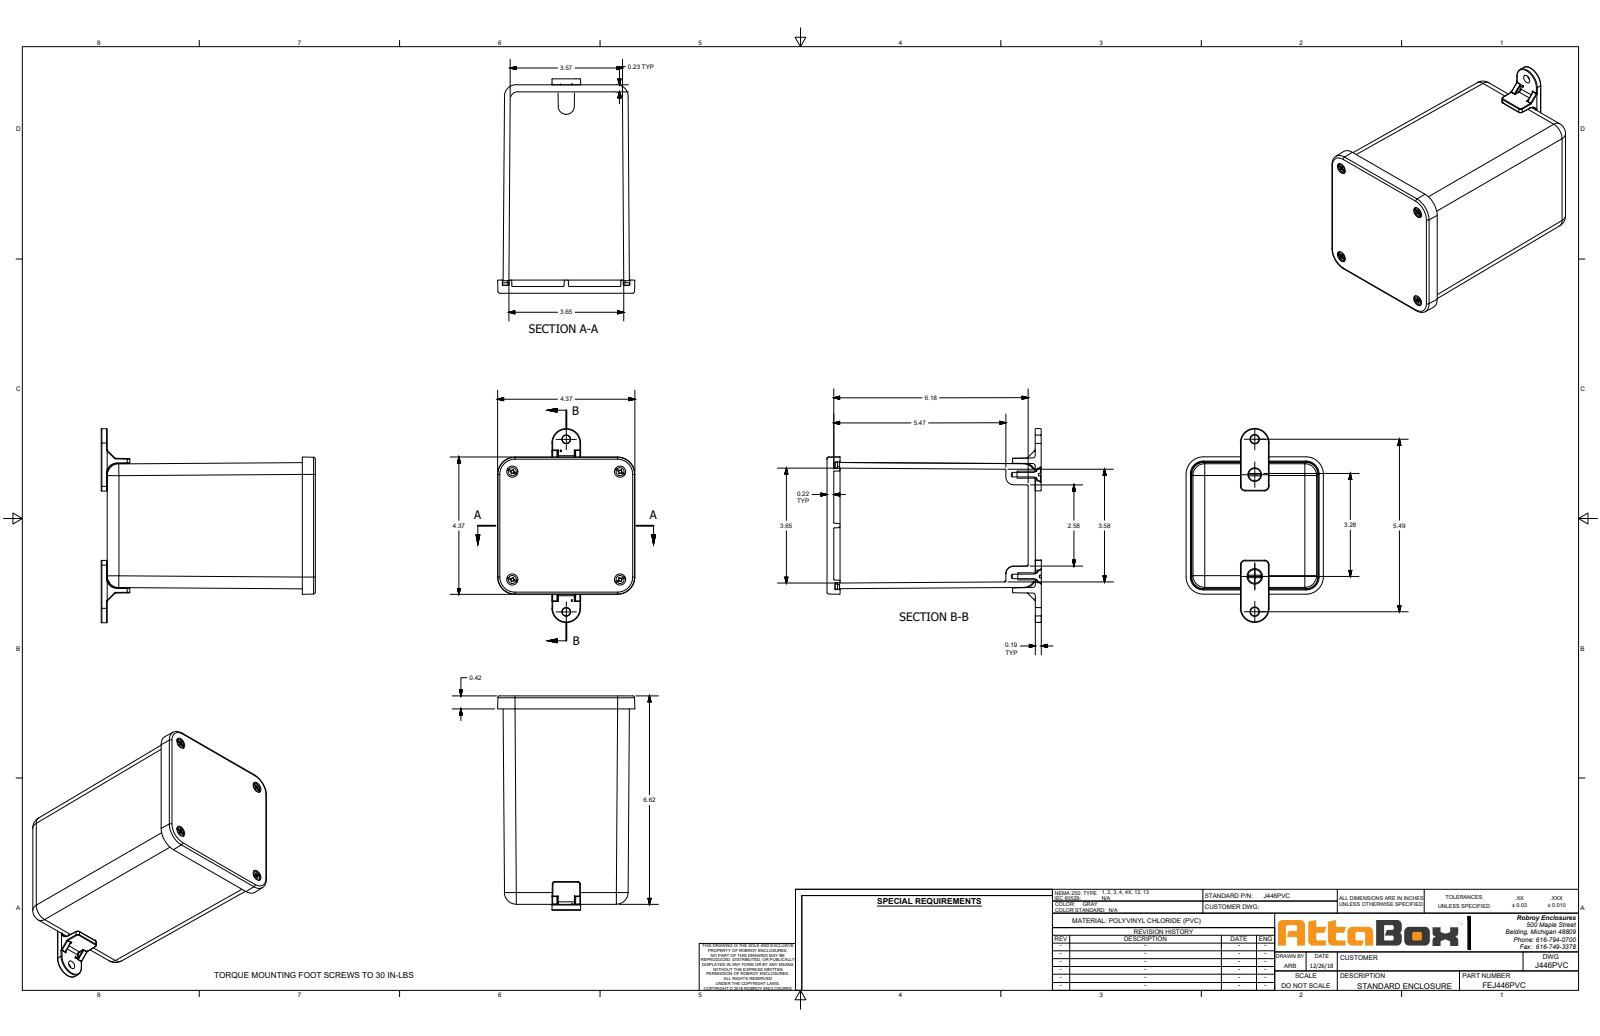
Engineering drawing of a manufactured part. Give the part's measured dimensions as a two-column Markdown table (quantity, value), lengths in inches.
| quantity | value |
| --- | --- |
| part name | J446PVC |
| STEP written by | SolidWorks 2018 (AUTOMOTIVE_DESIGN) |
| units | inches |
| bodies | 19 solids, 945 faces (361 planar, 278 cylindrical, 306 other) |
| overall size | 6.814 × 6.166 × 4.367 |
| volume | 28.15 in³ |
| surface area | 287.9 in² |
| round holes (diameter × count) | 0.2 × 6, 0.13 × 4, 0.18 × 4, 0.187 × 4, 0.223 × 4, 0.25 × 4, 0.335 × 4, 0.35 × 4, 0.166 × 2 |
| round bosses / shafts (diameter × count) | 0.354 × 4, 0.177 × 4, 0.187 × 3, 0.325 × 2, 0.325 × 2, 0.224 × 2 |
| partial cylindrical surfaces (radius × count) | 0.02 × 46, 0.025 × 36, 0.005 × 24, 0.031 × 12, 0.25 × 12, 0.375 × 8, 0.08 × 6, 0.06 × 4 |
| main face-to-face distances | 0.18, 6.624, 6.399, 6.409, 0.215, 0.225, 6.184, 6.369, 6.144, 0.04 |
| hole center spacings | 3.43, 1.718, 3.406, 3.406, 3.748, 3.748, 4.817, 4.834 |
